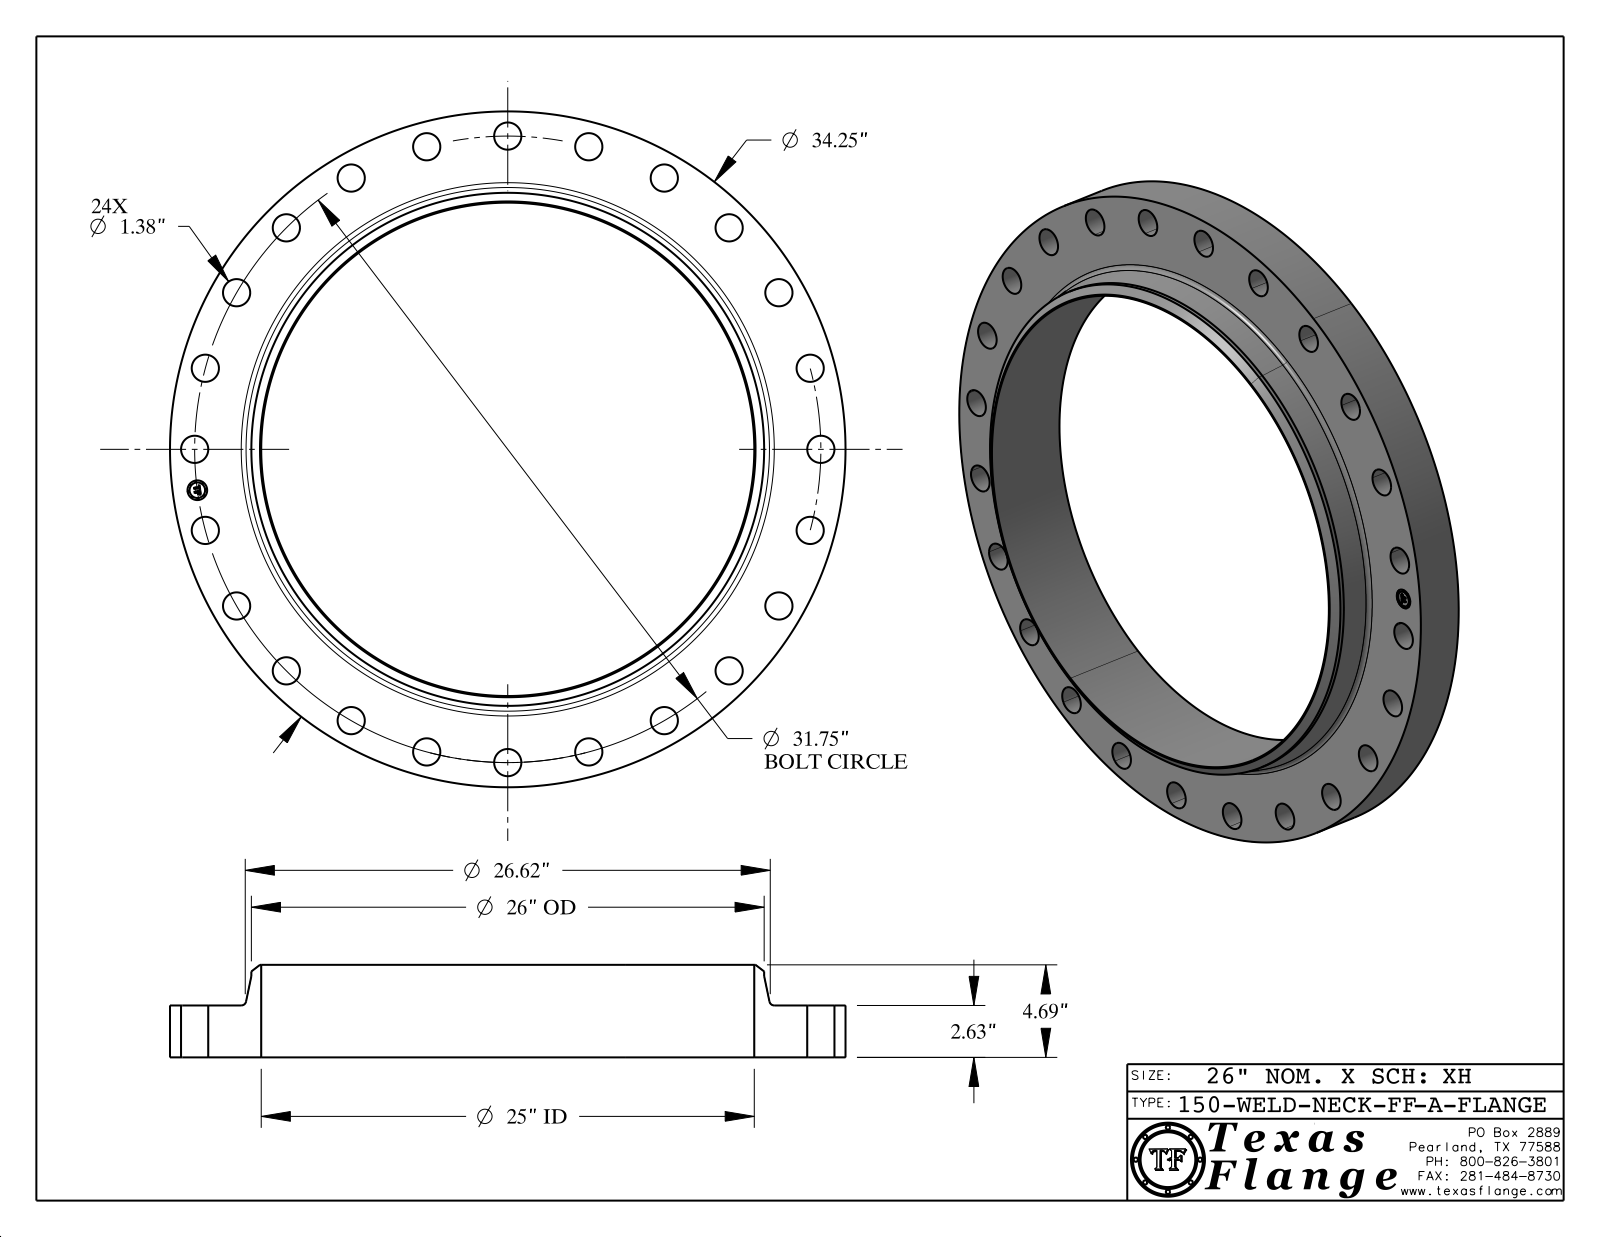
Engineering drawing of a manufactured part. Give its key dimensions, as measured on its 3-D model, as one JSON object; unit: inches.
{"part_name": "150-WELD-NECK-FF, Series A", "step_written_by": "CATIA V5 STEP AP214 (AUTOMOTIVE_DESIGN)", "units": "inches", "bodies": {"solids": 1, "faces": 448, "planar": 368, "cylindrical": 74, "other": 6}, "overall_size": [34.25, 34.25, 4.69], "volume_in3": 1134, "surface_area_in2": 1837, "round_holes": [[1.38, 24], [1, 1], [25, 1]], "round_bosses_or_shafts": [[0.061, 8], [34.25, 1], [26, 1], [0.788, 1]], "face_to_face_distances": [2.63, 4.69, 2.06, 2.615, 0.015, 2.075, 0.298, 0.292, 0.054, 0.193], "hole_center_spacings": [15.875, 15.875, 29.333, 27.496, 4.144, 8.217, 12.15, 19.328]}
